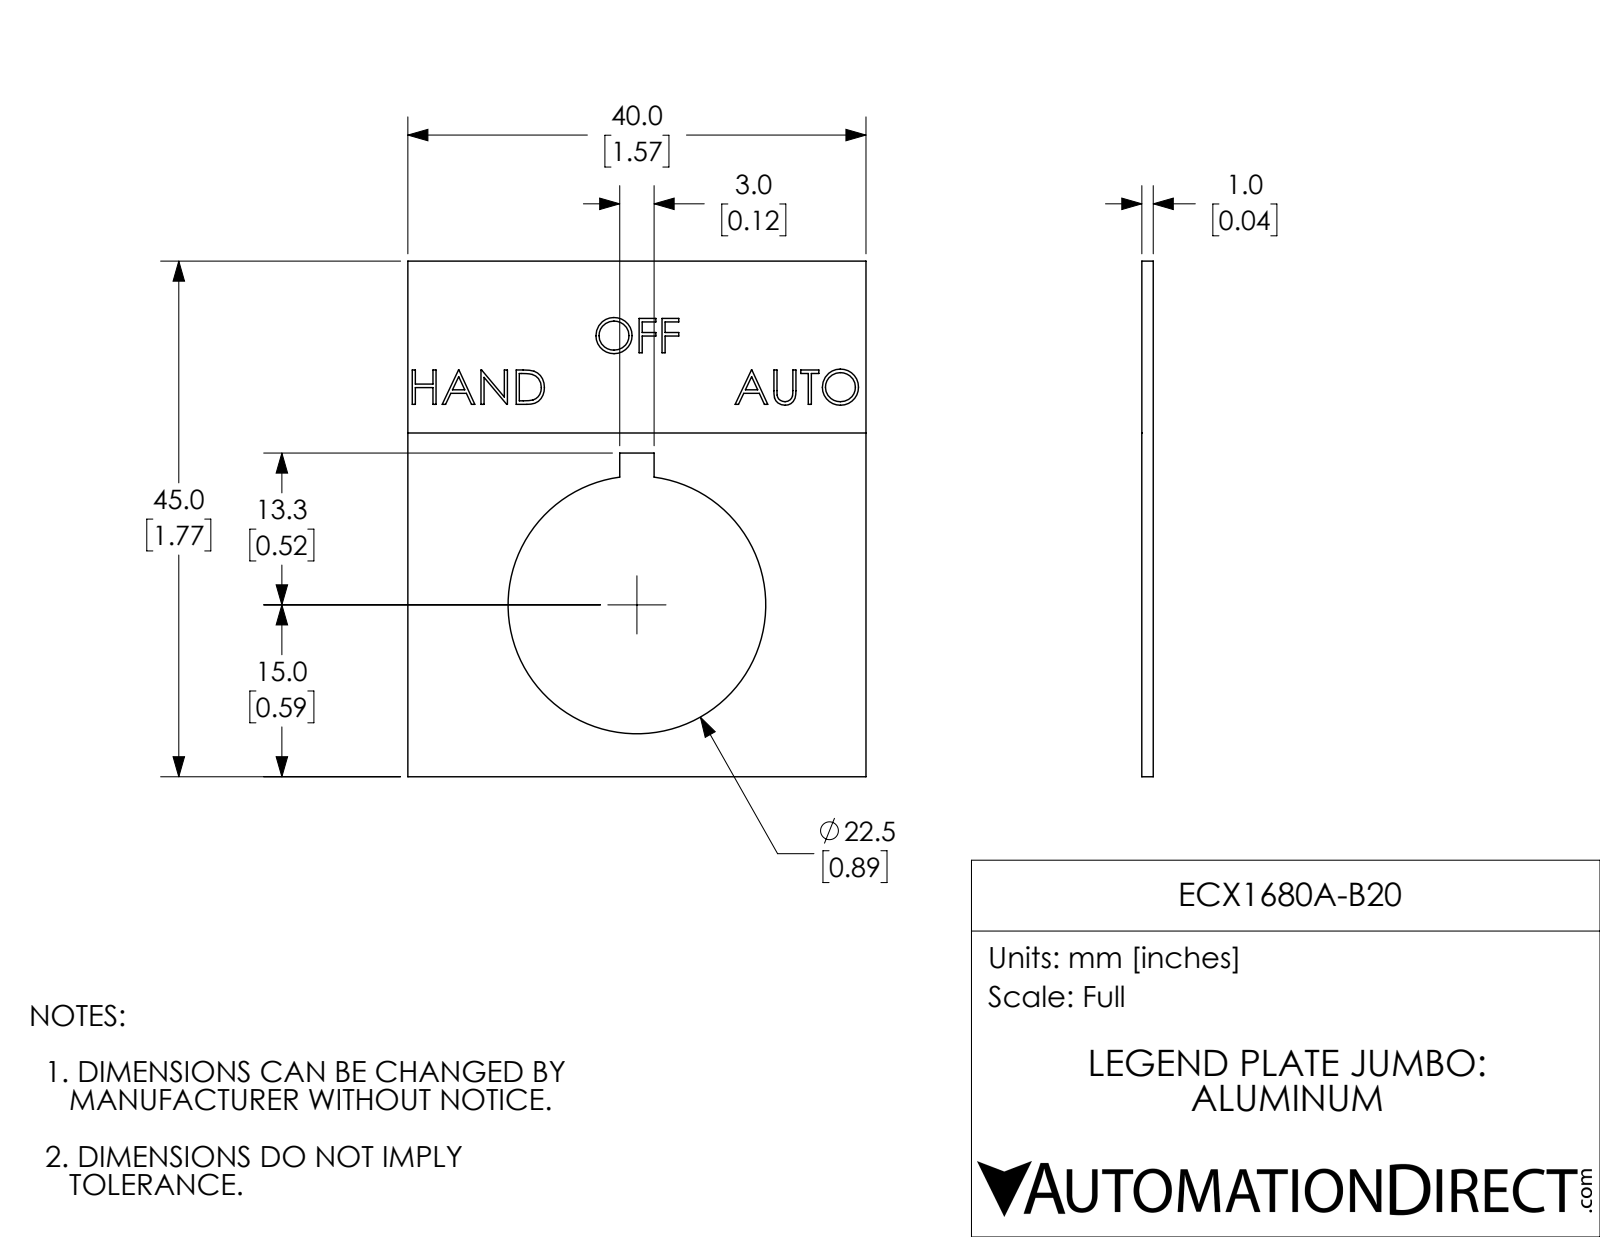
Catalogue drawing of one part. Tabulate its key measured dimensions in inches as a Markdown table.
| quantity | value |
| --- | --- |
| part name | ECX1680A-B20 |
| STEP written by | SolidWorks 2017 (AUTOMOTIVE_DESIGN) |
| units | inches |
| bodies | 1 solid, 144 faces (111 planar, 3 cylindrical, 30 other) |
| overall size | 1.772 × 1.575 × 0.039 |
| volume | 0.085 in³ |
| surface area | 4.709 in² |
| round holes (diameter × count) | 0.886 × 1 |
| main face-to-face distances | 0.039, 0.039, 1.575, 1.772, 0.728, 0.846, 1.112, 0.659, 0.118, 1.181 |
